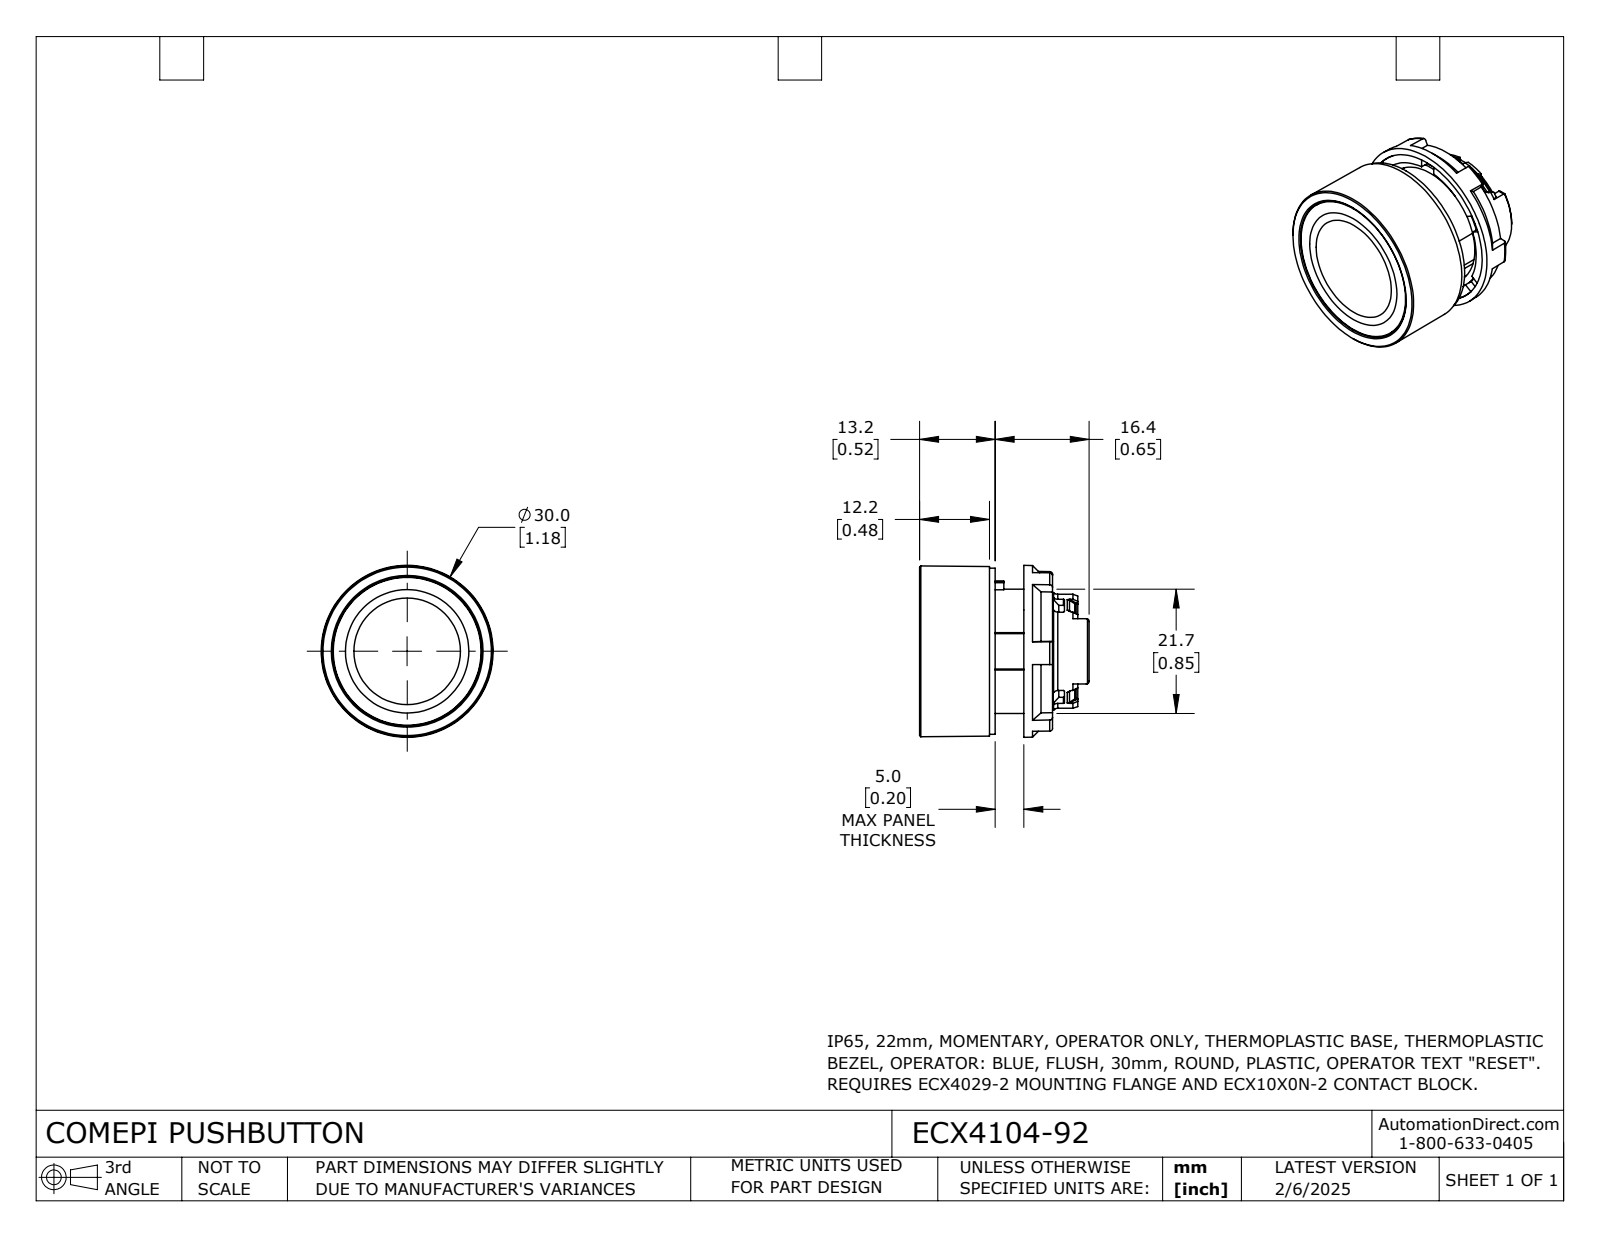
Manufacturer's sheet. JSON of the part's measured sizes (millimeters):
{"part_name": "ECX4104-92", "step_written_by": "SolidWorks 2024 (CONFIG_CONTROL_DESIGN)", "units": "millimeters", "bodies": {"solids": 3, "faces": 398, "planar": 134, "cylindrical": 111, "other": 153}, "overall_size": [30, 30, 29.6], "volume_mm3": 7730, "surface_area_mm2": 10680, "round_holes": [[13.5, 1], [18.1, 1], [22, 1]], "round_bosses_or_shafts": [[29, 1], [25.8, 1], [24.5, 1], [21.7, 1], [20.5, 1], [20, 1], [19, 1], [18.5, 1]], "partial_cylinders_radius": [[0.2, 24], [0.5, 8], [0.3, 2], [7.4, 1], [8.7, 1], [8.8, 1], [9.3, 1]], "face_to_face_distances": [10.4, 1, 11, 12, 6, 10, 5, 11.4, 13, 5.5]}
